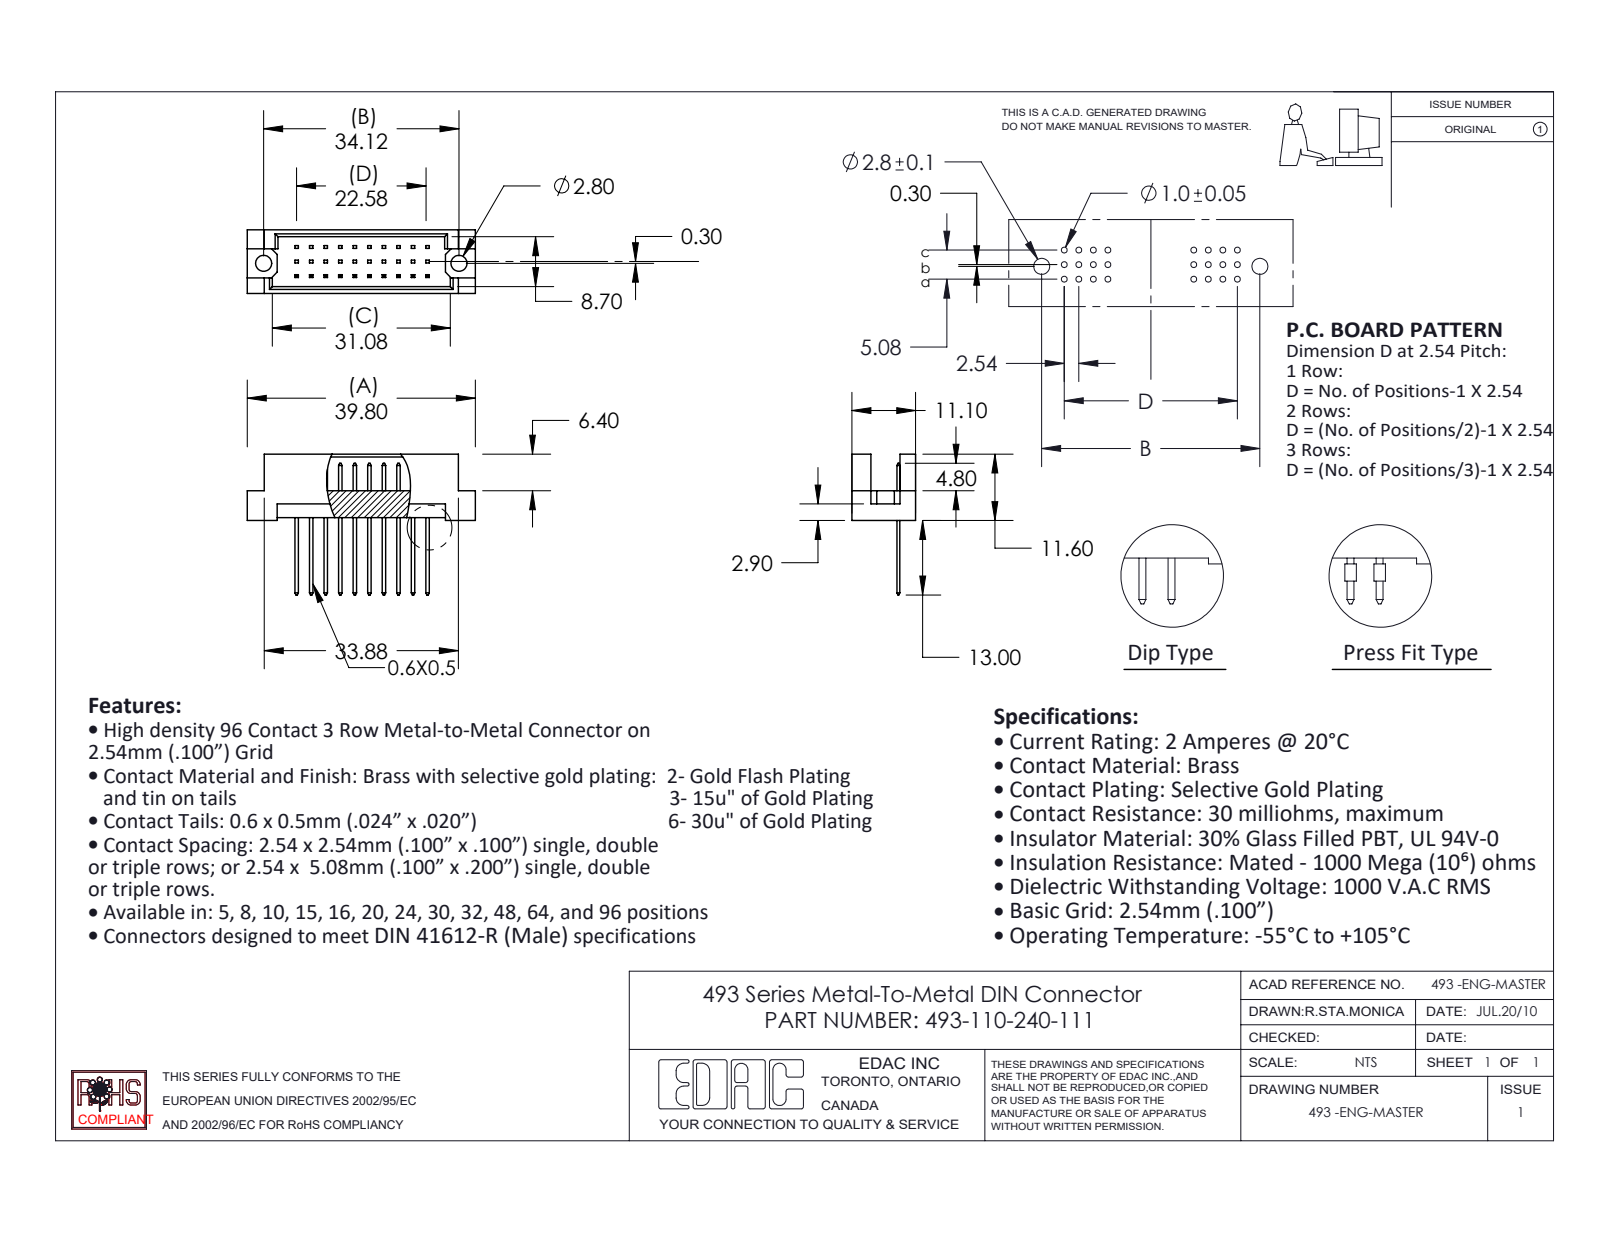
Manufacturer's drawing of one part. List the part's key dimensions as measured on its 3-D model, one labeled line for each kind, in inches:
Part name (STEP PRODUCT): 493-290_40; 493-110-240-111; 493 Part_30
STEP written by: SolidWorks 2020 (CONFIG_CONTROL_DESIGN)
Units: inches
Bodies: 11 solids, 312 faces (308 planar, 4 cylindrical, 0 other)
Overall size (bounding box): 1.567 × 0.969 × 0.437
Volume: 0.149 in³ · Surface area: 5.022 in²
Round holes (diameter × count): ⌀0.11 ×2
Main face-to-face distances: 0.047, 0.39, 0.437, 0.1, 0.02, 0.343, 0.2, 0.185, 0.109, 0.128
Hole centre spacings: 1.343
